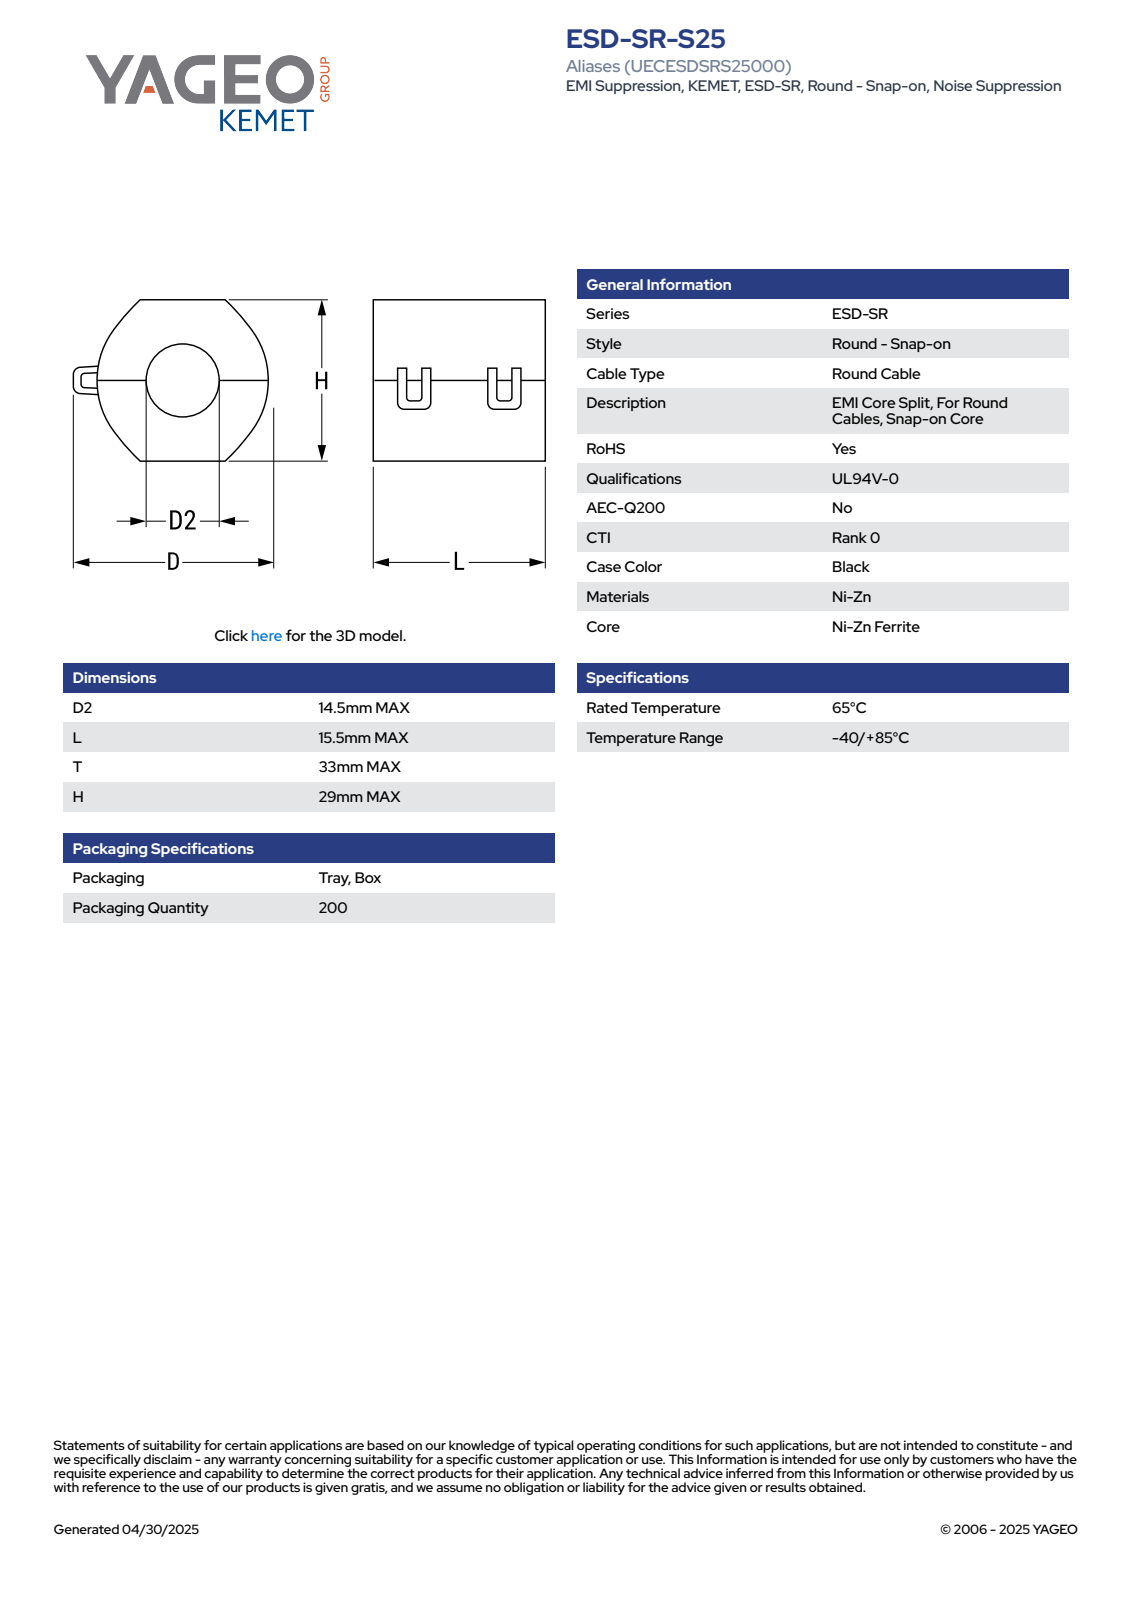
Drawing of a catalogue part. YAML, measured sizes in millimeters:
part_name: "EC_ESDSRS_D214.5L15.5T33H29"
step_written_by: "SolidWorks 2014 (AUTOMOTIVE_DESIGN)"
units: millimeters
bodies: {solids: 2, faces: 84, planar: 78, cylindrical: 6, other: 0}
overall_size: [33, 29, 15.5]
volume: 9764
surface_area: 4122
round_holes:
  - {diameter: 14.5, count: 1}
partial_cylinders:
  - {radius: 16.25, count: 1}
face_to_face_distances: [15.5, 14.49, 14.51, 29, 0.52, 1.88, 5.88, 9.62, 13.62, 4]
